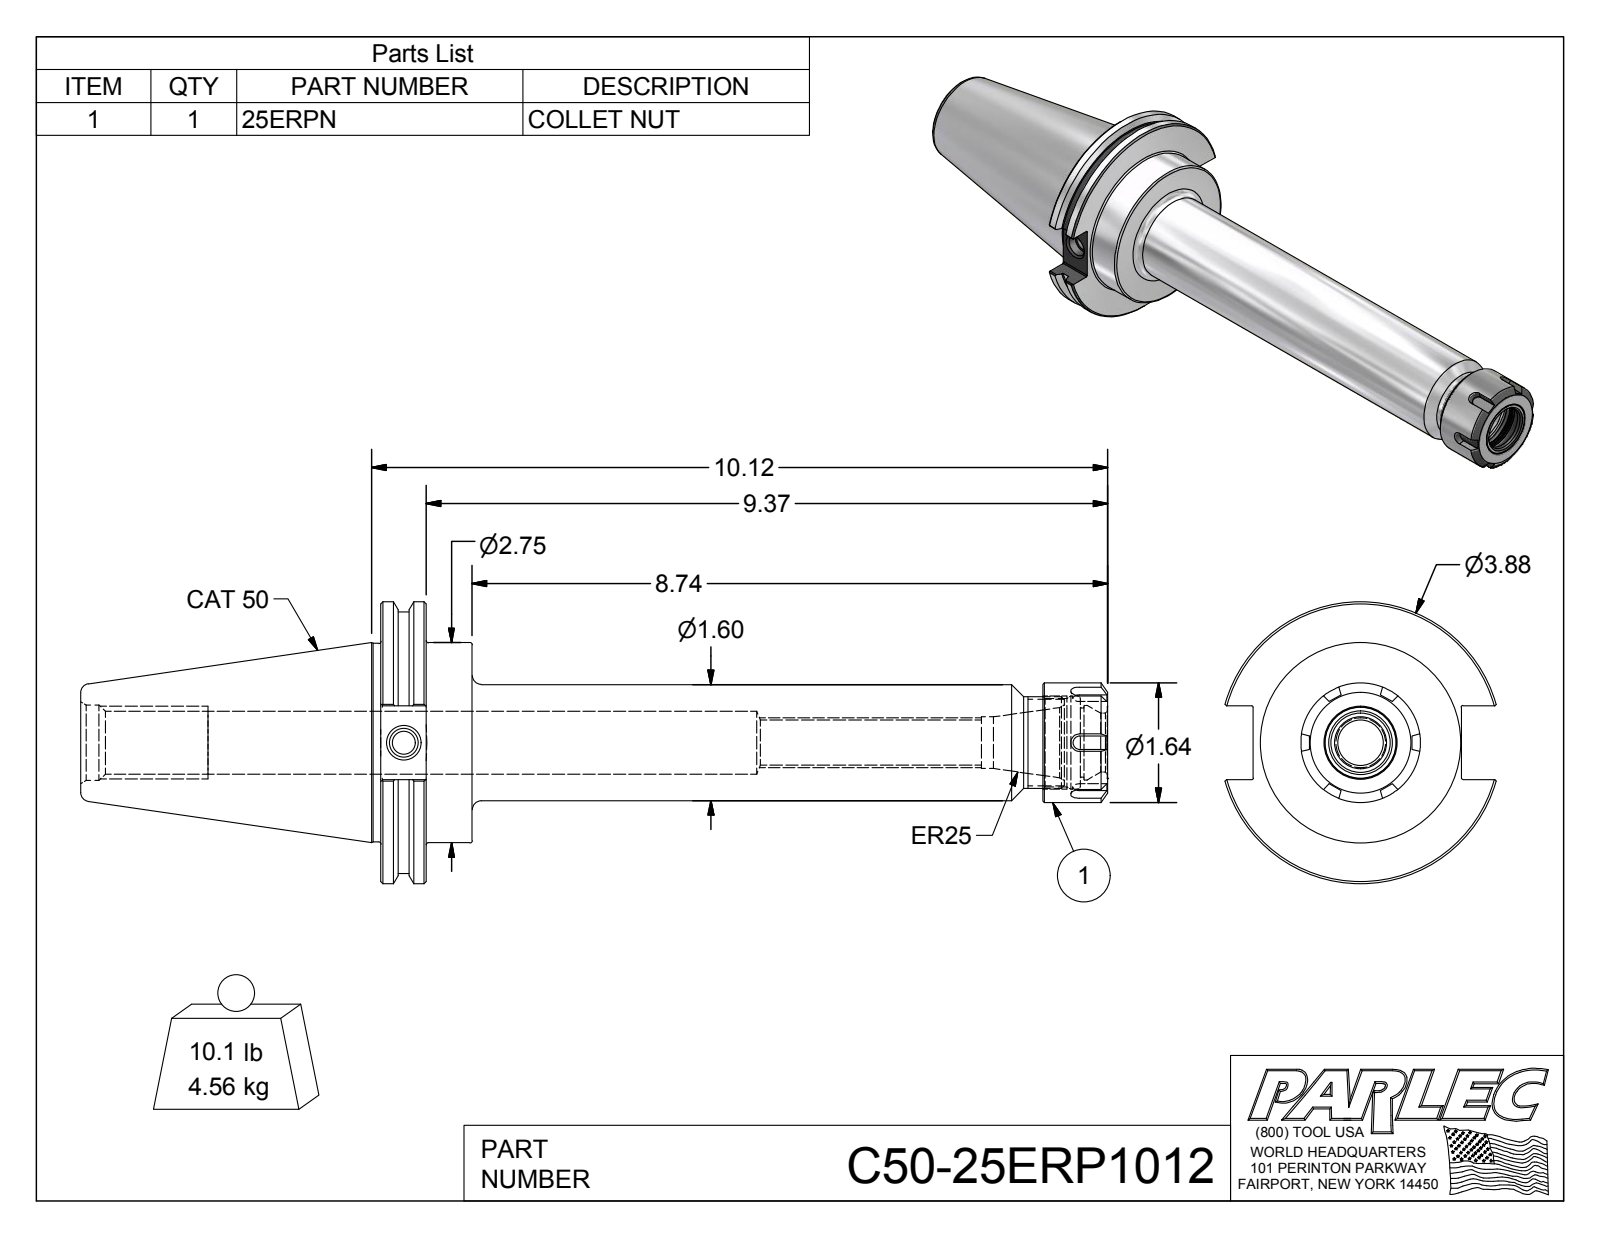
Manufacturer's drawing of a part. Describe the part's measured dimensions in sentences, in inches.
The part is named "C50-25ERP1012; C50-25ER10-1; 25ERPN". Its 3-D file was written by "Autodesk Inventor 2012 (AUTOMOTIVE_DESIGN)". It is 2 solids with 127 faces: 52 planar, 31 cylindrical and 44 other. Overall it measures 14.12 by 3.875 by 3.729 inches. Its volume is 35.62 cubic inches and its surface area 145 square inches. Round holes: 1 of diameter 0.315, 1 of diameter 0.399, 1 of diameter 0.62, 1 of diameter 0.71, 1 of diameter 0.811, 1 of diameter 0.864, 1 of diameter 0.865, 1 of diameter 0.95, 1 of diameter 1.027, 1 of diameter 1.038, 1 of diameter 1.217, 1 of diameter 1.28. Round bosses or shafts: 1 of diameter 3.875, 1 of diameter 3.594, 1 of diameter 2.75, 1 of diameter 2.73, 1 of diameter 1.643, 1 of diameter 1.595, 1 of diameter 1.26. Partial cylindrical surfaces (rounded edges, fillets, slot ends): 8 of radius 0.02. The main face-to-face distances are 0.625, 1.255, 0.63, 9.995, 9.37, 8.74, 9.102, 8.477, 7.847, 0.893.
